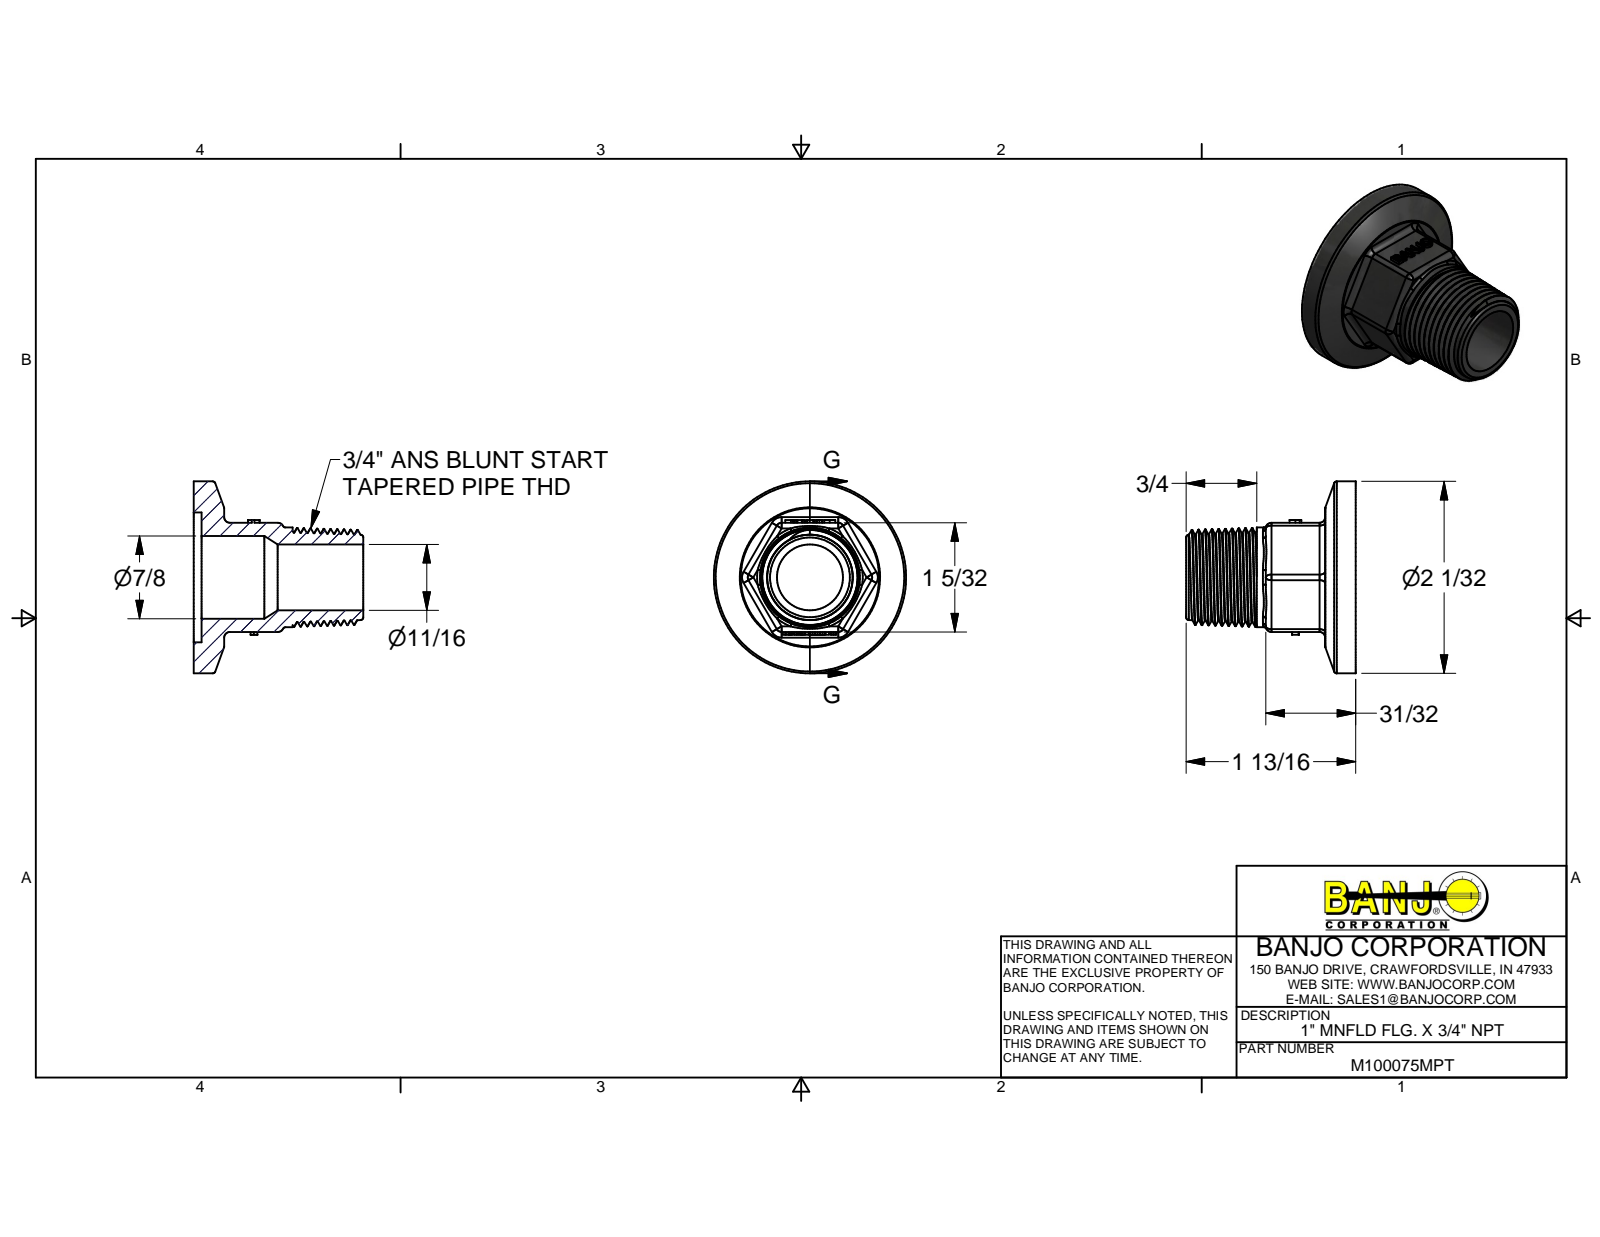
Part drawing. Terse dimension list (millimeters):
name: M100075MPT
written by: Autodesk Inventor 2014 (AUTOMOTIVE_DESIGN)
unit: mm
bodies: 1 solid, 299 faces (142 planar, 24 cylindrical, 133 other)
size: 51.82 × 51.82 × 45.72
volume: 23 000 mm³; area: 11 788 mm²
holes: 1× ⌀17.78, 1× ⌀22.35, 1× ⌀35.05
bosses: 1× ⌀51.82, 1× ⌀26.92
rounds: 18× R1.52, 1× R7.04
face distances: 29.46, 2.13, 8.24, 6.11, 37.48, 43.59, 45.72, 19.05, 18.43, 24.54
